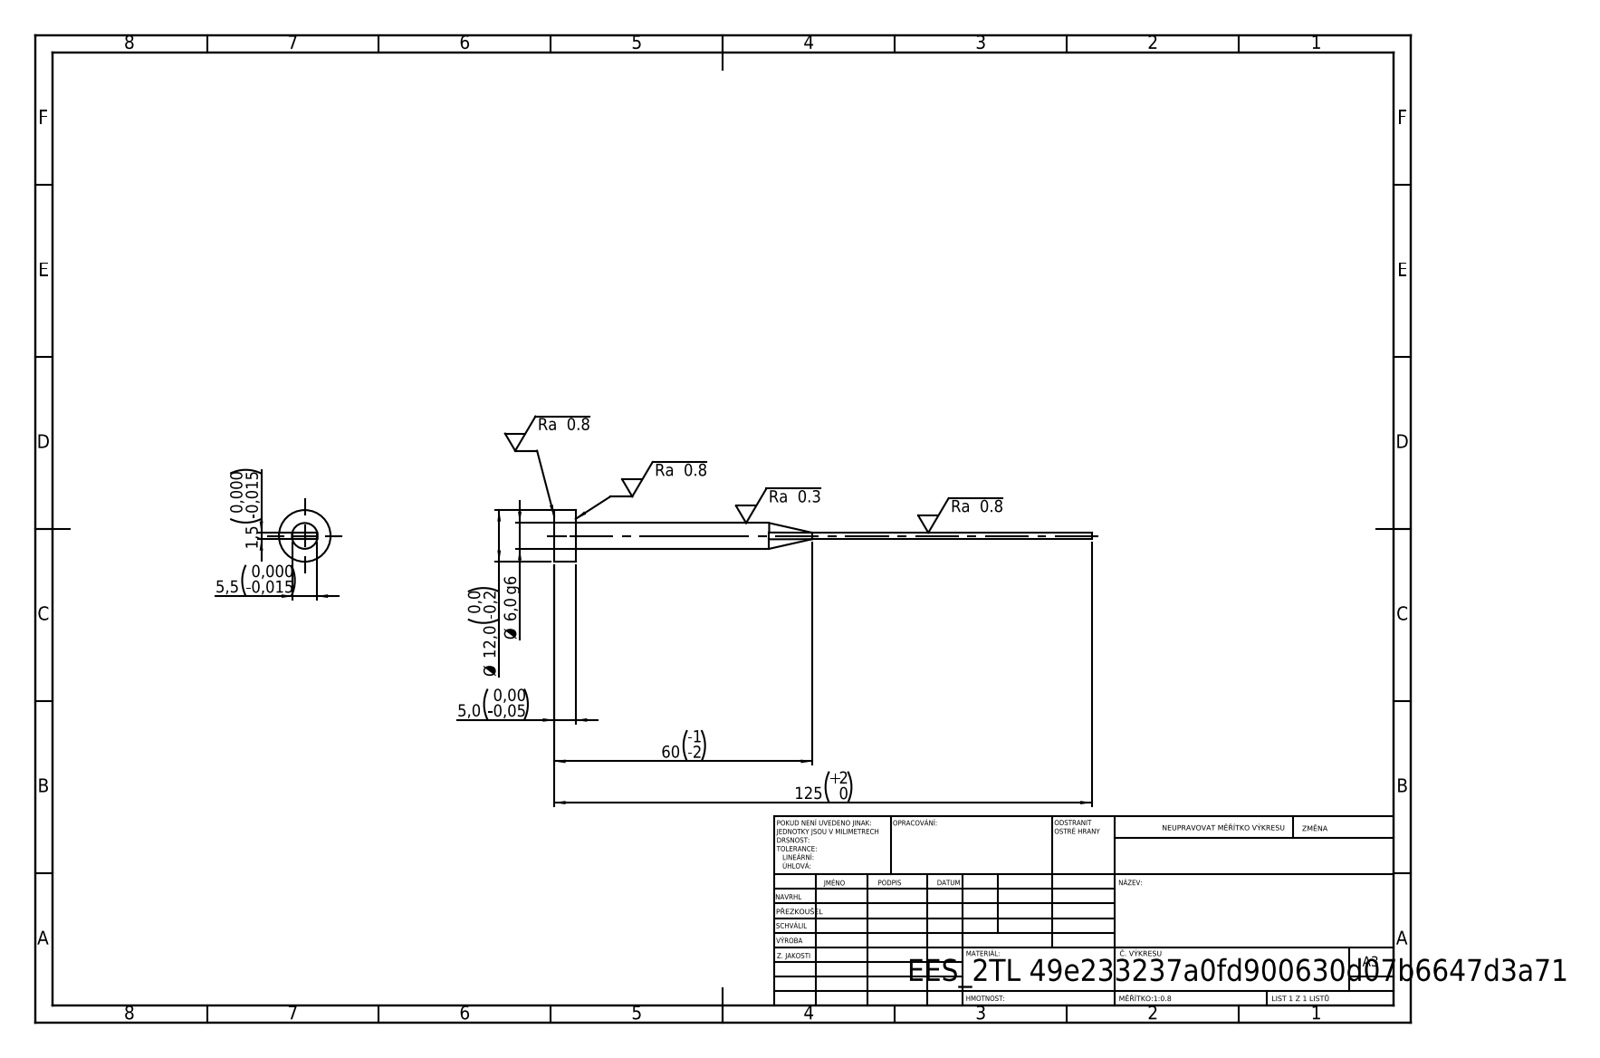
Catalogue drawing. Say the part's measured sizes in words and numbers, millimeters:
Its 3-D file was written by "SolidWorks 2019 (CONFIG_CONTROL_DESIGN)". It is 1 solid with 15 faces: 7 planar, 4 cylindrical and 4 other. Overall it measures 125 by 12 by 12 millimeters. Its volume is 2 550 cubic millimeters and its surface area 2 312 square millimeters. Round bosses or shafts: 1 of diameter 12, 1 of diameter 6. The main face-to-face distances are 1.5, 5.5, 5, 125, 120.
